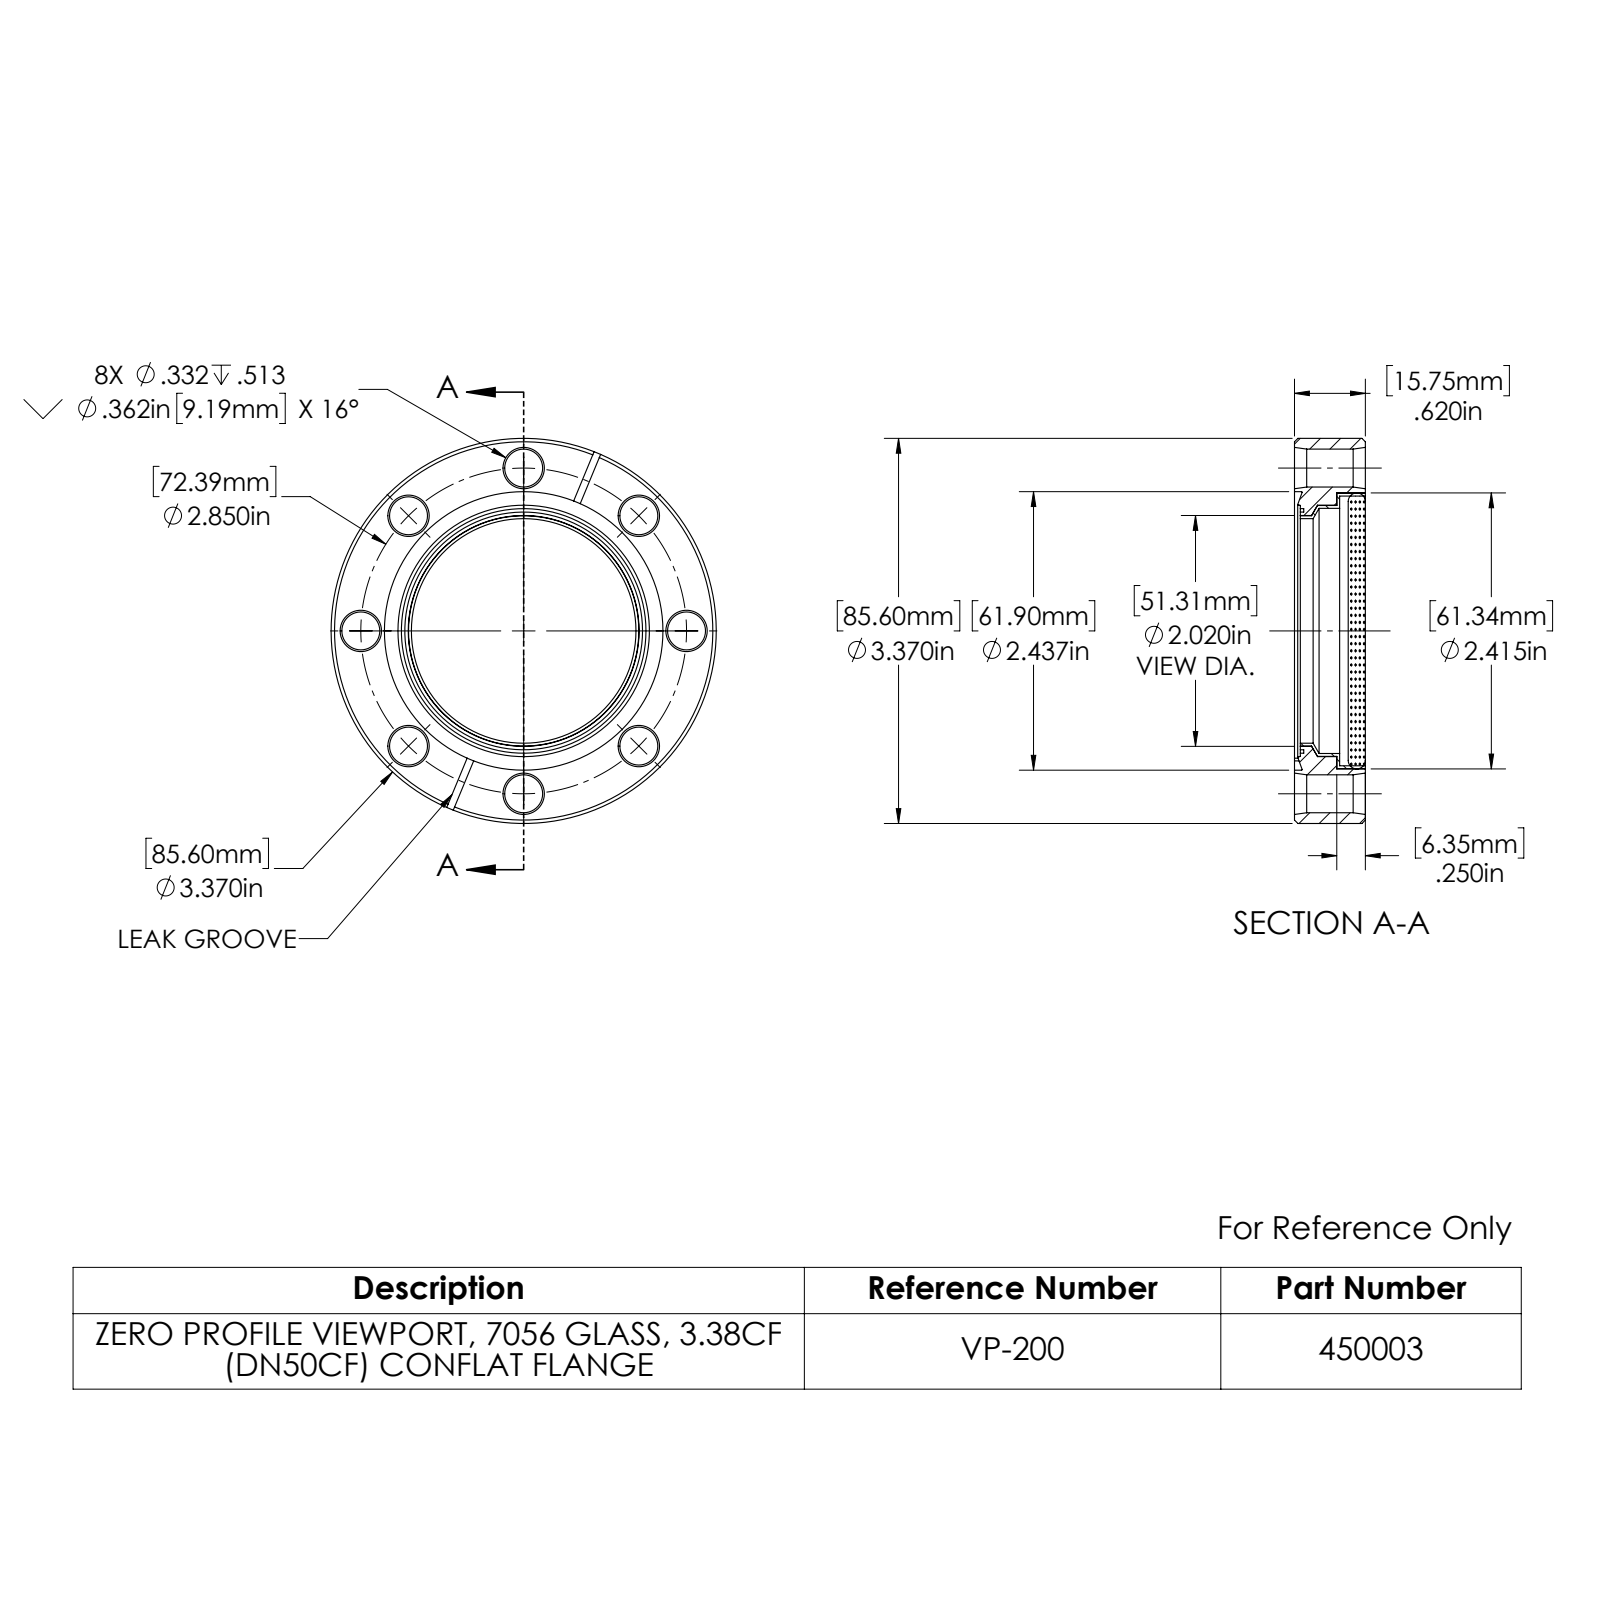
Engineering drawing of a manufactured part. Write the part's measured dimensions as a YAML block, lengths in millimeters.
part_name: "450003"
step_written_by: "SolidWorks 2022 (CONFIG_CONTROL_DESIGN)"
units: millimeters
bodies: {solids: 3, faces: 118, planar: 17, cylindrical: 46, other: 55}
overall_size: [85.6, 85.6, 15.7]
volume: 54780
surface_area: 30050
round_holes:
  - {diameter: 8.4, count: 8}
  - {diameter: 49.9, count: 1}
  - {diameter: 51.3, count: 1}
  - {diameter: 54.4, count: 1}
  - {diameter: 54.5, count: 1}
  - {diameter: 55.9, count: 1}
  - {diameter: 59.9, count: 1}
  - {diameter: 61.3, count: 1}
  - {diameter: 61.9, count: 1}
round_bosses_or_shafts:
  - {diameter: 85.6, count: 1}
  - {diameter: 61.2, count: 1}
  - {diameter: 55.8, count: 1}
  - {diameter: 52.8, count: 1}
  - {diameter: 51.2, count: 1}
partial_cylinders:
  - {radius: 31.8, count: 2}
face_to_face_distances: [3.8, 11.9, 15.7, 9.4, 2.5, 6.4, 10, 0.6, 1.9, 5.7]
hole_center_spacings: [27.7, 66.9, 36.2, 36.2, 51.2, 51.2, 72.4, 72.4]
